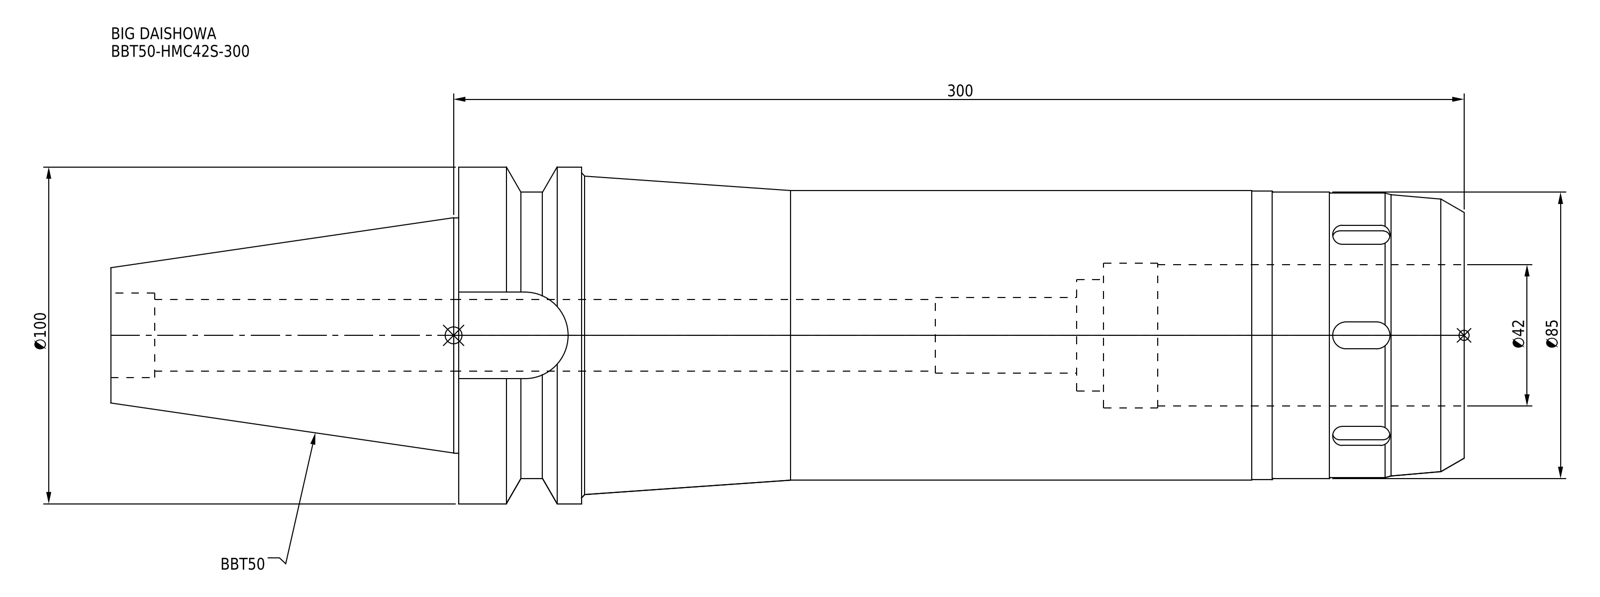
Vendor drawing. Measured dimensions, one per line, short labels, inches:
name: BBT50-HMC42S-300
written by: CREO PARAMETRIC BY PTC INC, 2016380 (AUTOMOTIVE_DESIGN)
unit: in
bodies: 1 solid, 106 faces (40 planar, 46 cylindrical, 20 other)
size: 15.819 × 3.937 × 3.937
volume: 108.3 in³; area: 230.1 in²
holes: 1× ⌀0.835, 1× ⌀0.886, 1× ⌀0.984, 1× ⌀1.299, 1× ⌀1.654, 1× ⌀1.693
bosses: 1× ⌀3.937, 1× ⌀3.386, 1× ⌀3.374, 1× ⌀3.346, 1× ⌀3.327, 1× ⌀2.75
rounds: 12× R0.157, 1× R0.506
face distances: 11.752, 15.819, 4.067, 2.787, 0.315, 4.213, 7.539, 11.606, 10.315, 6.102
